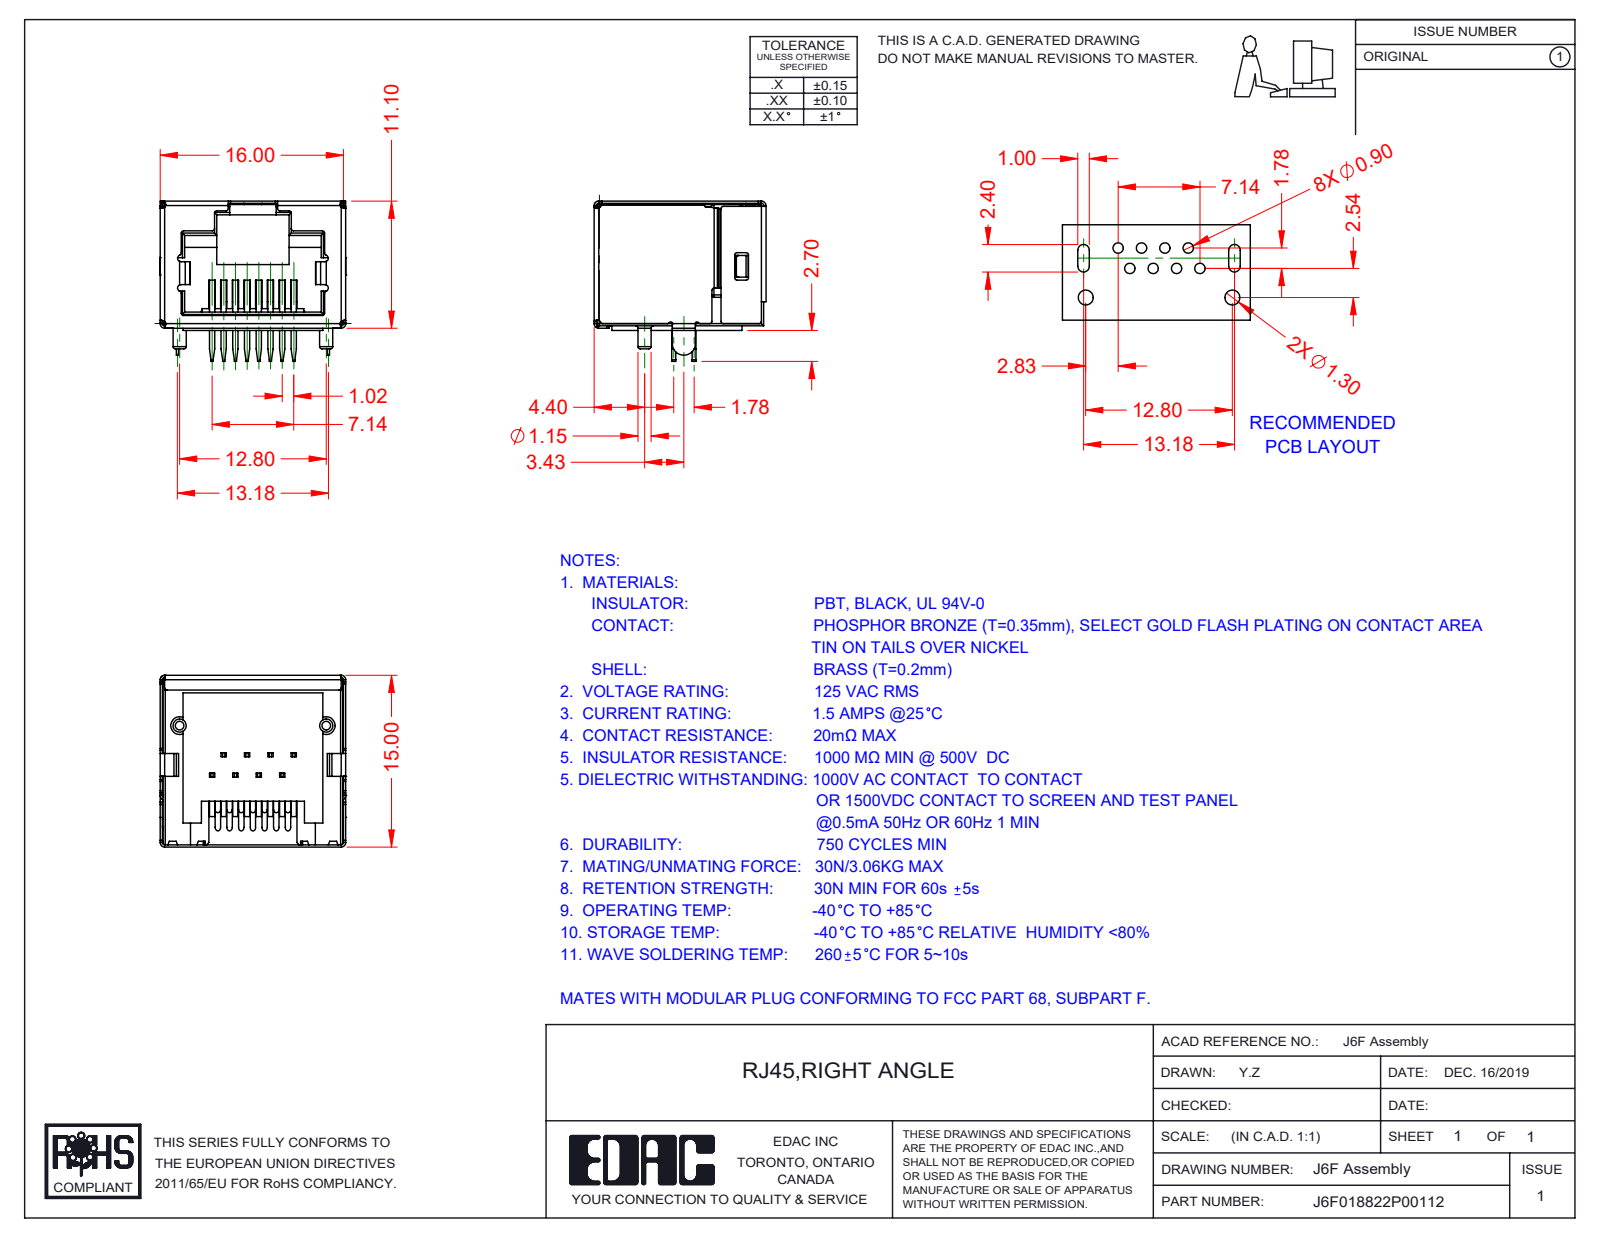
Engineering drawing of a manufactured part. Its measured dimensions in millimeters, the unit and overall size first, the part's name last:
Units: millimetres
Overall size (bounding box): 16.2 × 15 × 14
Round bosses / shafts (diameter × count): ⌀1.15 ×2
Partial cylindrical surfaces — rounded edges, fillets, slot ends (radius × count): R0.2 ×77, R0.4 ×24, R0.3 ×20, R0.5 ×9, R0.23 ×7, R0.15 ×5, R0.1 ×4, R1 ×3
Main face-to-face distances: 15.75, 16, 15.95, 11, 15.7, 9.7, 11.1, 16.2, 15.8, 1.2
Volume: 1 336 mm³ · Surface area: 3 711 mm²
Bodies: 10 solids, 960 faces (695 planar, 223 cylindrical, 42 other)
Part name (STEP PRODUCT): 6F Shield; 6F Contacts; J6F018822P00112; 6F Insulator
STEP written by: SolidWorks 2016 (CONFIG_CONTROL_DESIGN)
